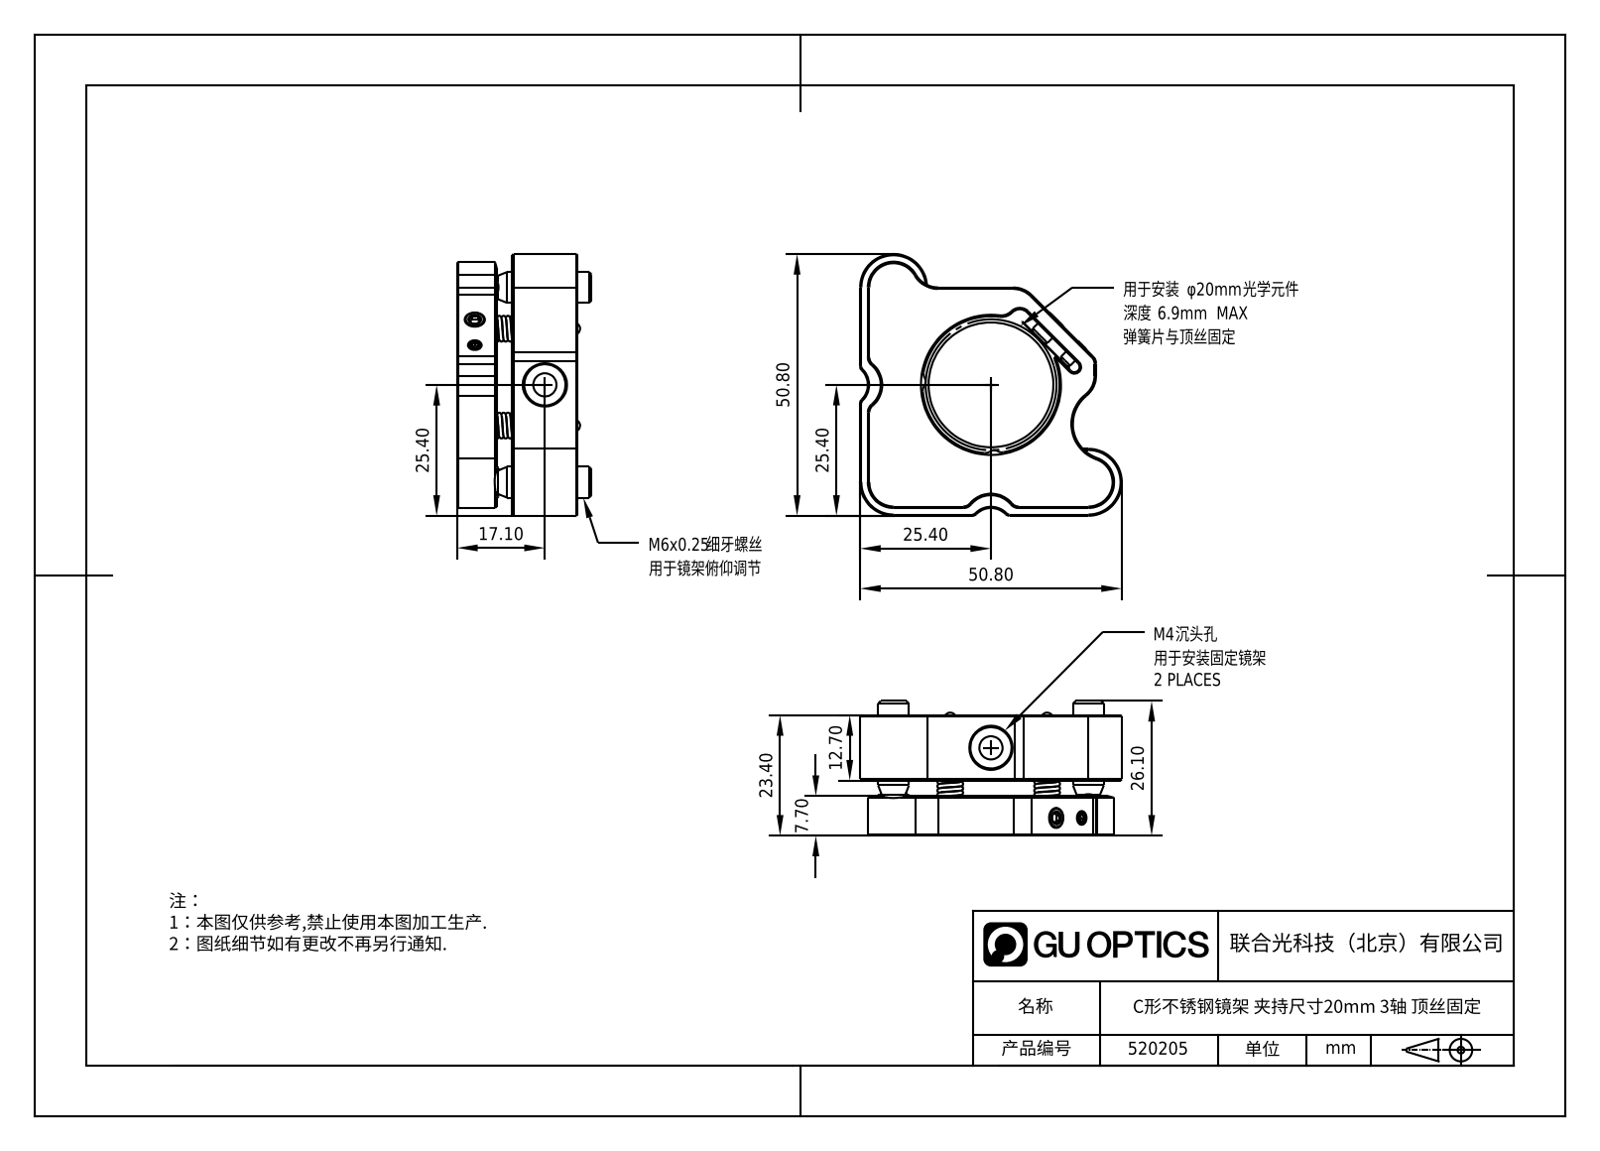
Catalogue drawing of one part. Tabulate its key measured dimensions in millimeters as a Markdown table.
| quantity | value |
| --- | --- |
| part name | 1.1.20.29-ZJO-20-3; 36.1，440c不锈钢滚珠_36.1.6_GZ-B4; 不锈钢方形压片_32.6.12-QY-1305-0.2; DXS-0625标准型六角调节器 _3.2.2.15.1-DXS-0625-20 (+4 more) |
| STEP written by | SolidWorks 2021 (CONFIG_CONTROL_DESIGN) |
| units | millimeters |
| bodies | 29 solids, 702 faces (235 planar, 171 cylindrical, 296 other) |
| overall size | 50.8 × 50.8 × 26.13 |
| volume | 22 144 mm³ |
| surface area | 16 867 mm² |
| round holes (diameter × count) | 2.5 × 4, 6 × 4, 3.99 × 3, 5.75 × 3, 6.35 × 3, 2 × 2, 4.5 × 2, 8 × 2, 2.05 × 1, 3.3 × 1, 18.8 × 1 |
| round bosses / shafts (diameter × count) | 4 × 7, 3 × 4, 2 × 4, 6 × 3, 2.5 × 1 |
| partial cylindrical surfaces (radius × count) | 5 × 10, 1 × 9, 1.05 × 8, 1.5 × 6, 2 × 6, 6.5 × 3, 4 × 2, 3 × 1 |
| main face-to-face distances | 7.7, 3, 10.7, 12.7, 15.7, 23.4, 1.5, 11.5, 13, 0.5 |
| hole center spacings | 18.8, 26.73, 5, 8, 11, 13.86, 15.68, 17.39 |
